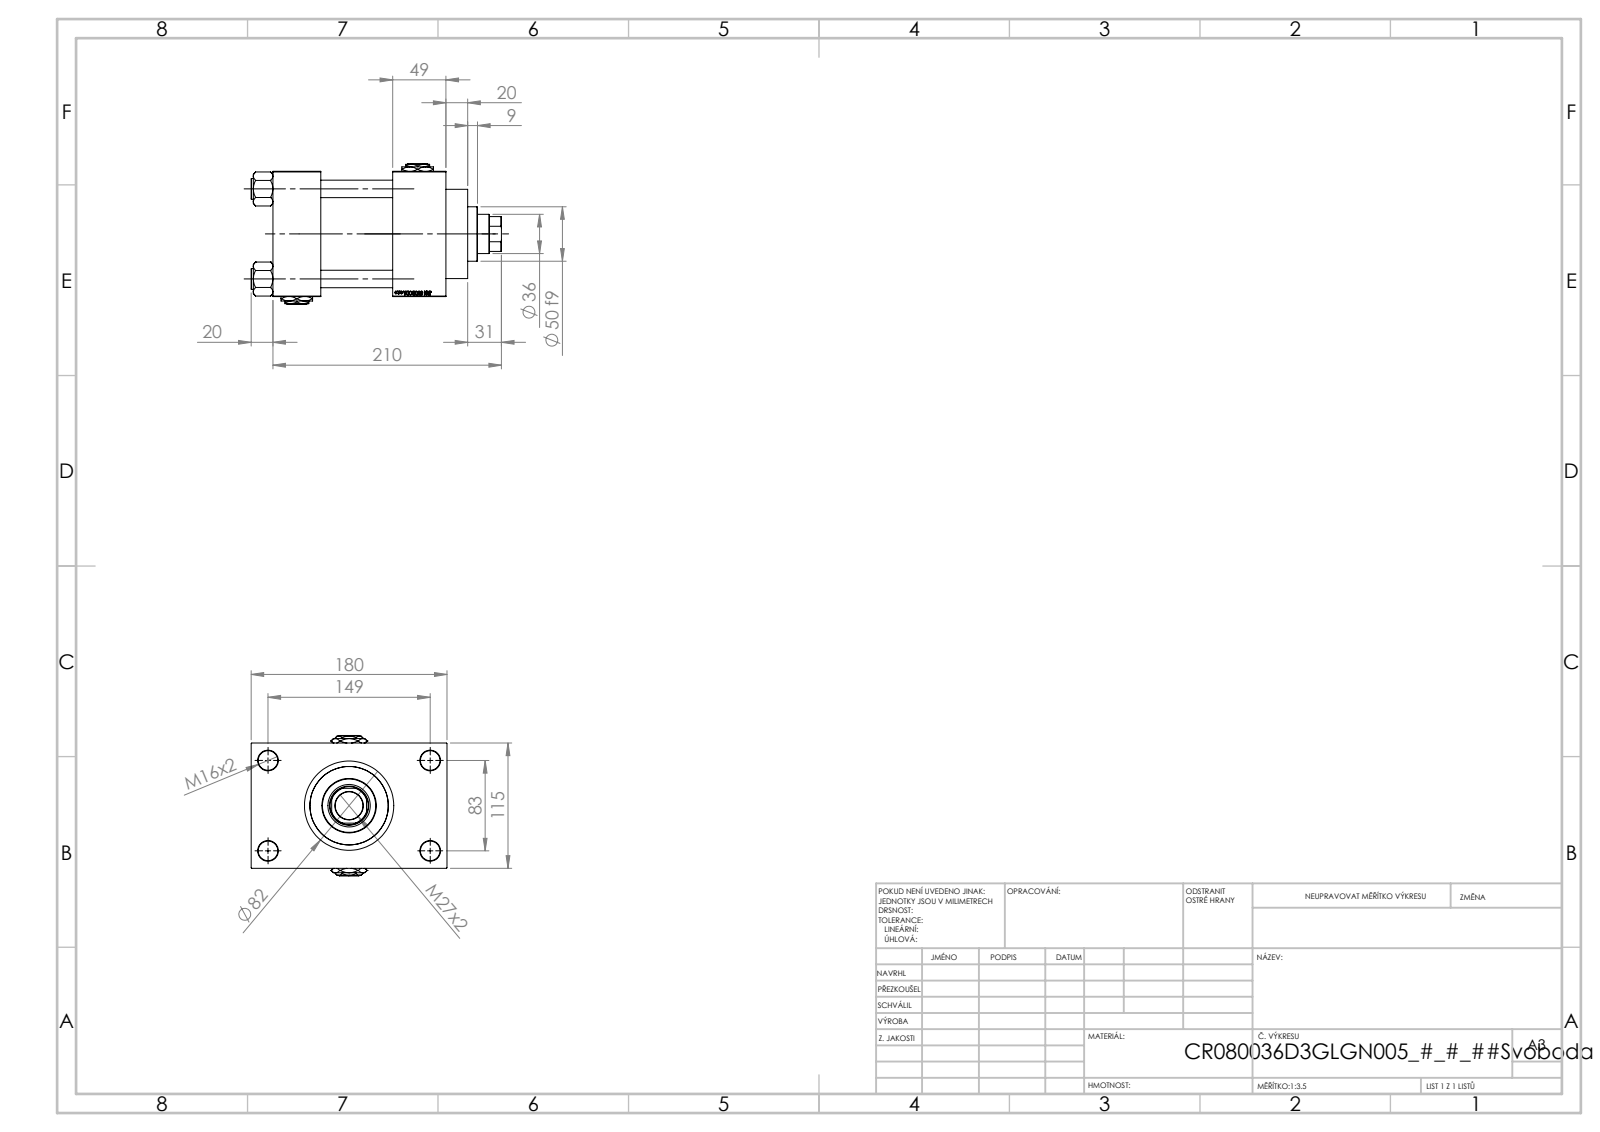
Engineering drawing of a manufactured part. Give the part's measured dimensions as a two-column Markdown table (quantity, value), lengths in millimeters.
| quantity | value |
| --- | --- |
| part name | V215CR_VCP_D; V215CR_D_Body; NUT_M5_D; V215_VC_A (+2 more) |
| STEP written by | SolidWorks 2019 (CONFIG_CONTROL_DESIGN) |
| units | millimeters |
| bodies | 13 solids, 1236 faces (589 planar, 89 cylindrical, 558 other) |
| overall size | 230 × 180 × 129 |
| volume | 2 005 000 mm³ |
| surface area | 297 927 mm² |
| round holes (diameter × count) | 16 × 4, 18 × 4, 7 × 2, 26.44 × 2, 35 × 2, 25.5 × 1, 36 × 1, 39 × 1, 61 × 1, 72 × 1, 80 × 1 |
| round bosses / shafts (diameter × count) | 19 × 4, 86 × 1, 82 × 1, 50 × 1 |
| partial cylindrical surfaces (radius × count) | 17.5 × 1 |
| main face-to-face distances | 115, 66, 110, 49, 44, 159, 147.5, 32.5, 20, 69 |
| hole center spacings | 33.15, 58.48, 82.7, 85.28, 89.24, 115.85, 142.43, 83 |
